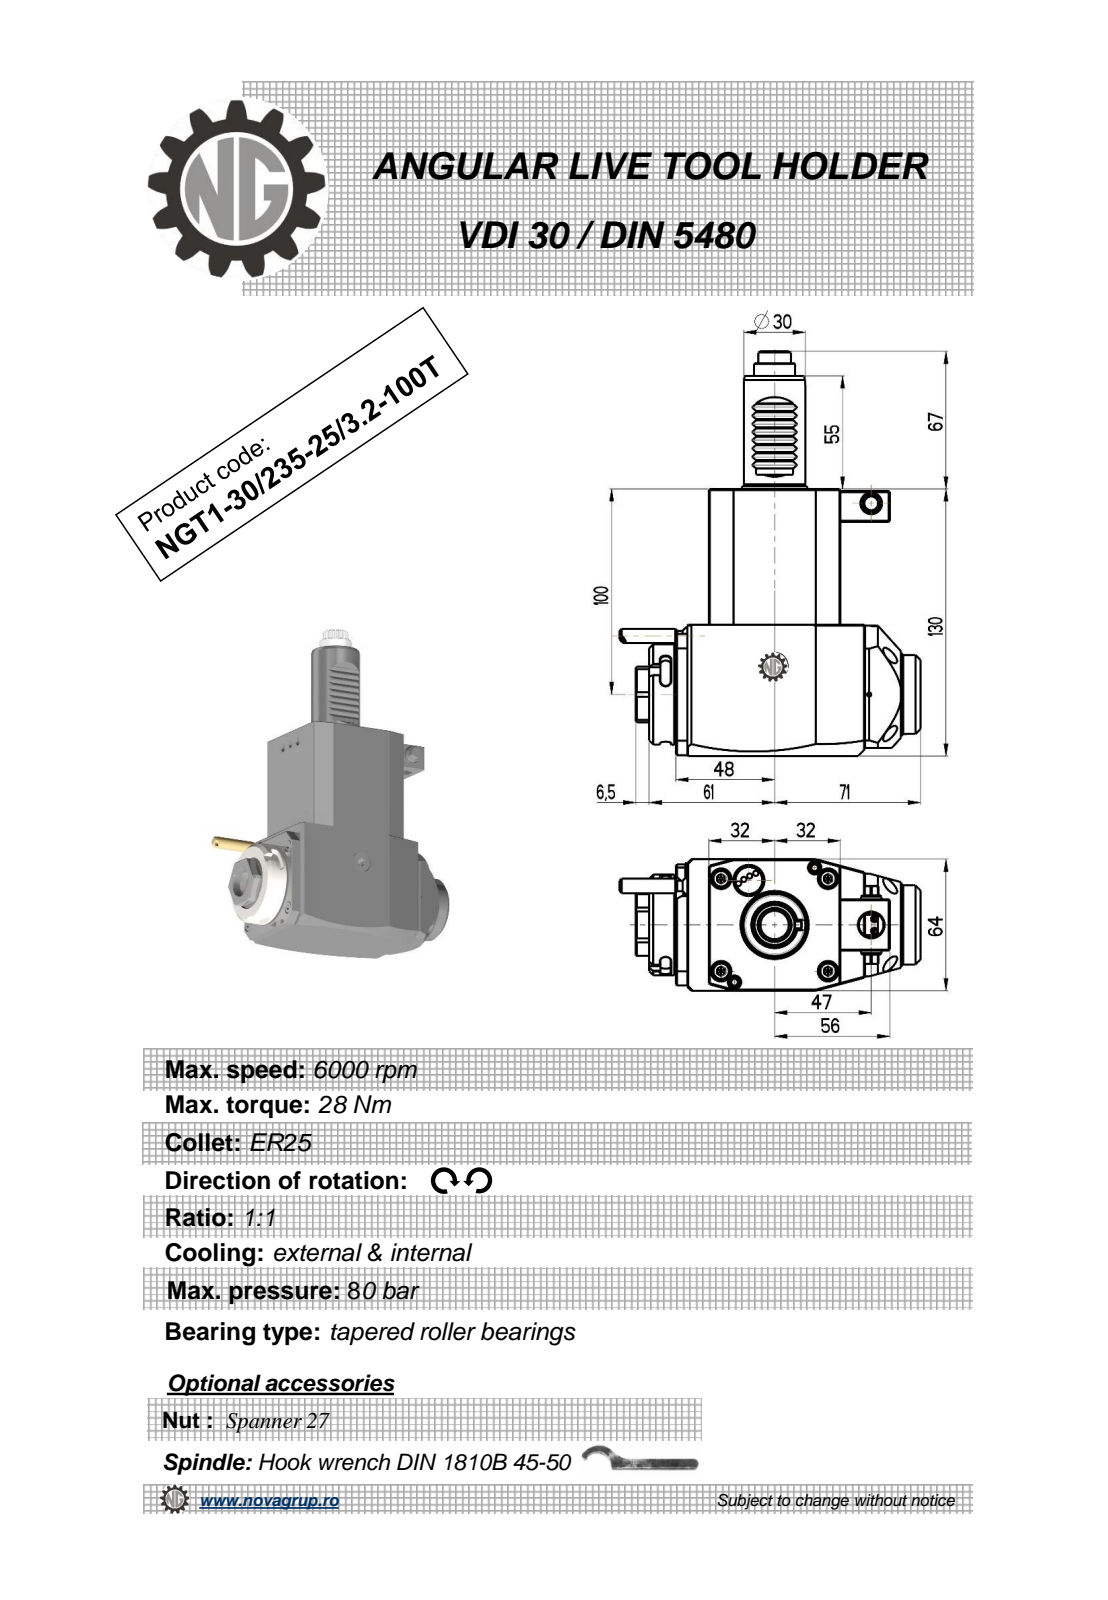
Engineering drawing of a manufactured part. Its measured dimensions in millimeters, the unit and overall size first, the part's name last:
Units: millimetres
Overall size (bounding box): 197 × 146.38 × 64
Round holes (diameter × count): ⌀2.5 ×1, ⌀3 ×1, ⌀9.5 ×1, ⌀12 ×1, ⌀18 ×1
Round bosses / shafts (diameter × count): ⌀8 ×2, ⌀49 ×1, ⌀42 ×1, ⌀38.5 ×1, ⌀30 ×1, ⌀20 ×1, ⌀10 ×1, ⌀7 ×1
Partial cylindrical surfaces — rounded edges, fillets, slot ends (radius × count): R1.98 ×36, R0.3 ×8, R2.5 ×6, R180 ×2, R3.85 ×1, R4.25 ×1, R4.5 ×1, R7.08 ×1
Main face-to-face distances: 64, 130, 16, 80, 72.18, 13, 66, 93, 29, 132
Hole centre spacings: 34.25, 65.8, 91.5
Volume: 750 794 mm³ · Surface area: 62 908 mm²
Bodies: 1 solid, 433 faces (188 planar, 155 cylindrical, 90 other)
Part name (STEP PRODUCT): NGT1_30_235_25_3_2_100T
STEP written by: PRO/ENGINEER BY PARAMETRIC TECHNOLOGY CORPORATION, 2010280 (CONFIG_CONTROL_DESIGN)
